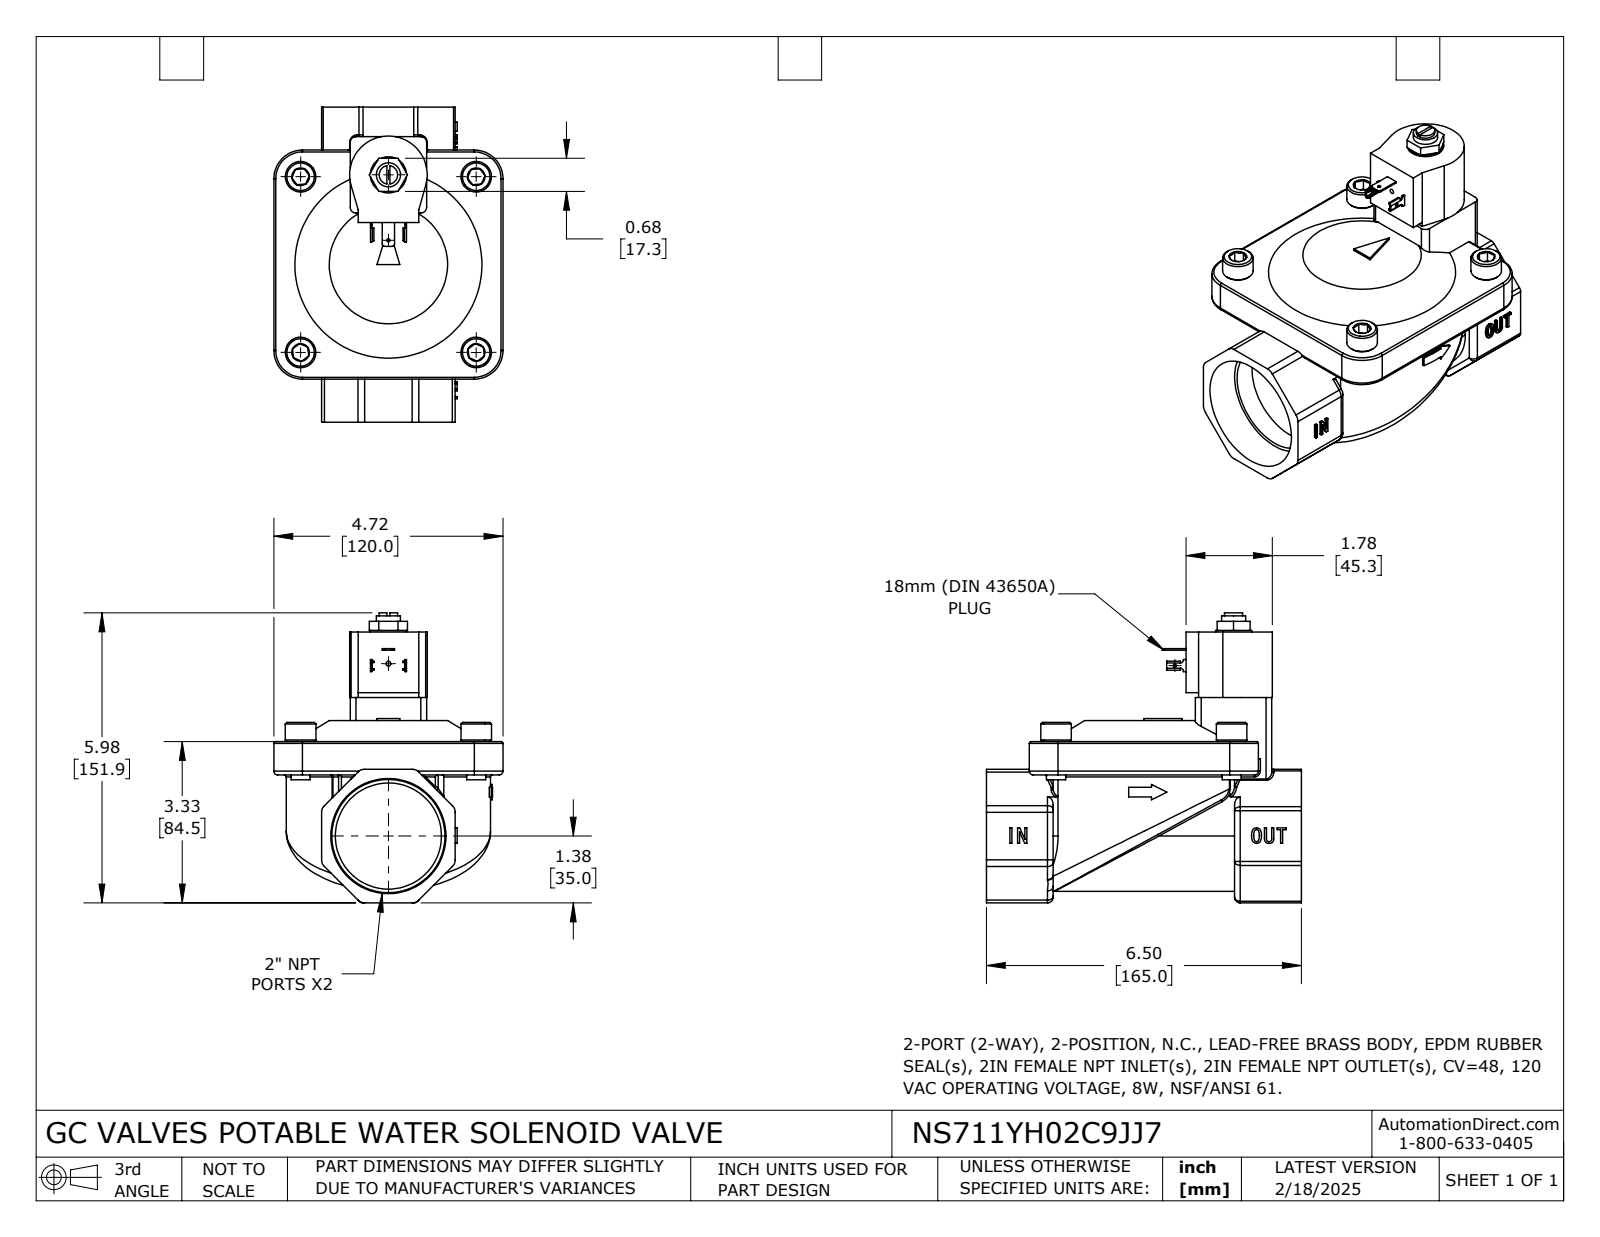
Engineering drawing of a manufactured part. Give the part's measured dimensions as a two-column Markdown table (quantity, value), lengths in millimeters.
| quantity | value |
| --- | --- |
| part name | NS711YH02C9JJ7 |
| STEP written by | SolidWorks 2024 (CONFIG_CONTROL_DESIGN) |
| units | millimeters |
| bodies | 1 solid, 474 faces (206 planar, 135 cylindrical, 133 other) |
| overall size | 165 × 151.87 × 120 |
| volume | 916 779 mm³ |
| surface area | 94 911 mm² |
| round holes (diameter × count) | 1.68 × 1, 1.7 × 1, 2.53 × 1, 55.58 × 1 |
| round bosses / shafts (diameter × count) | 16 × 4, 10 × 4, 18.95 × 1, 12.67 × 1, 9.65 × 1 |
| partial cylindrical surfaces (radius × count) | 3 × 28, 1 × 21, 5 × 10, 0.15 × 4, 1.04 × 4, 2 × 4, 15 × 4, 1.27 × 2 |
| main face-to-face distances | 17.5, 69.99, 95, 11, 40, 28.5, 25, 70, 120, 142.5 |
| hole center spacings | 90.26 |
